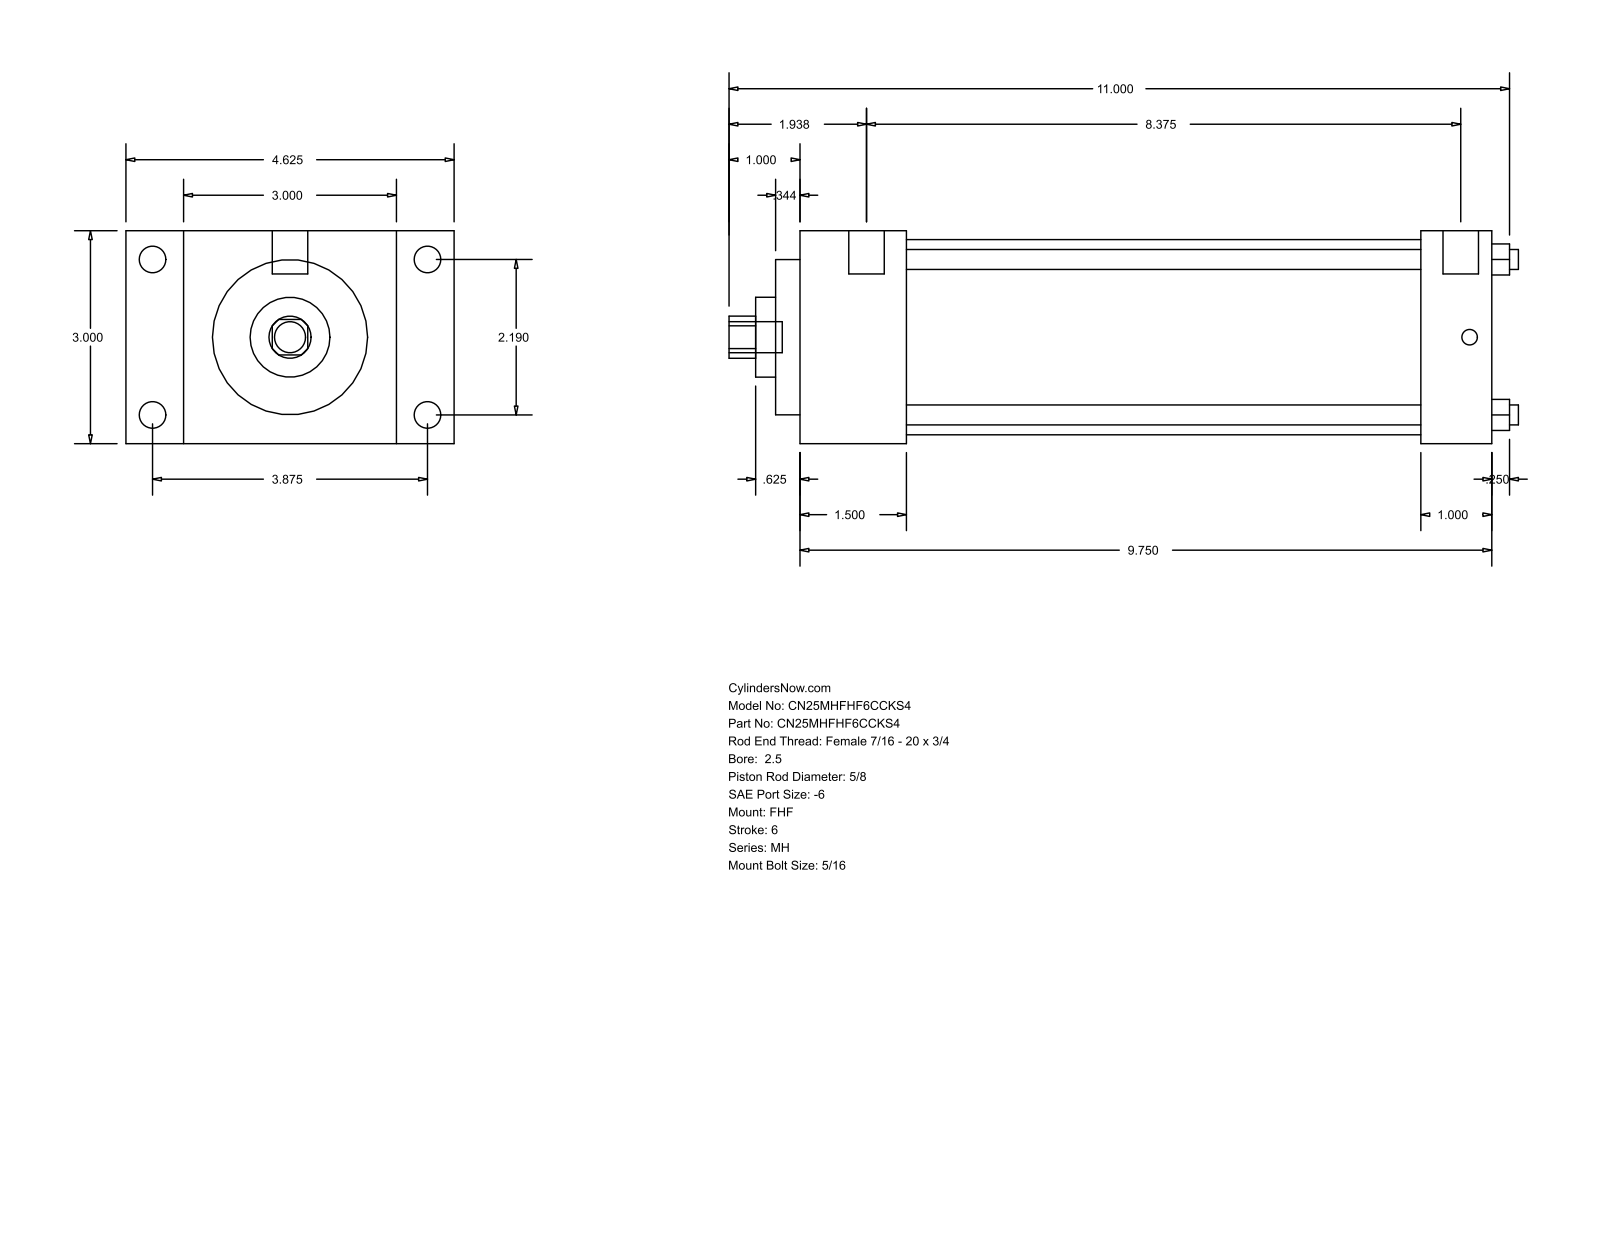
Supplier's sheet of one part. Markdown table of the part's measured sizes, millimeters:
| quantity | value |
| --- | --- |
| part name | MH_FHF__0250_0.625 |
| STEP written by | GSSL Pune (CONFIG_CONTROL_DESIGN) |
| units | millimeters |
| bodies | 0 solids, 90 faces (61 planar, 29 cylindrical, 0 other) |
| overall size | 282.57 × 117.47 × 76.2 |
| round holes (diameter × count) | 7.14 × 4, 15.88 × 1, 28.57 × 1, 55.55 × 1, 69.85 × 1 |
| round bosses / shafts (diameter × count) | 9.53 × 4, 5.56 × 4, 12.7 × 2, 11.11 × 1 |
| partial cylindrical surfaces (radius × count) | 7.54 × 1 |
| main face-to-face distances | 76.2, 247.65, 38.1, 209.55, 20.64, 96.84, 117.48, 25.4, 222.25, 184.15 |
| hole center spacings | 39.33, 55.62, 78.66 |
